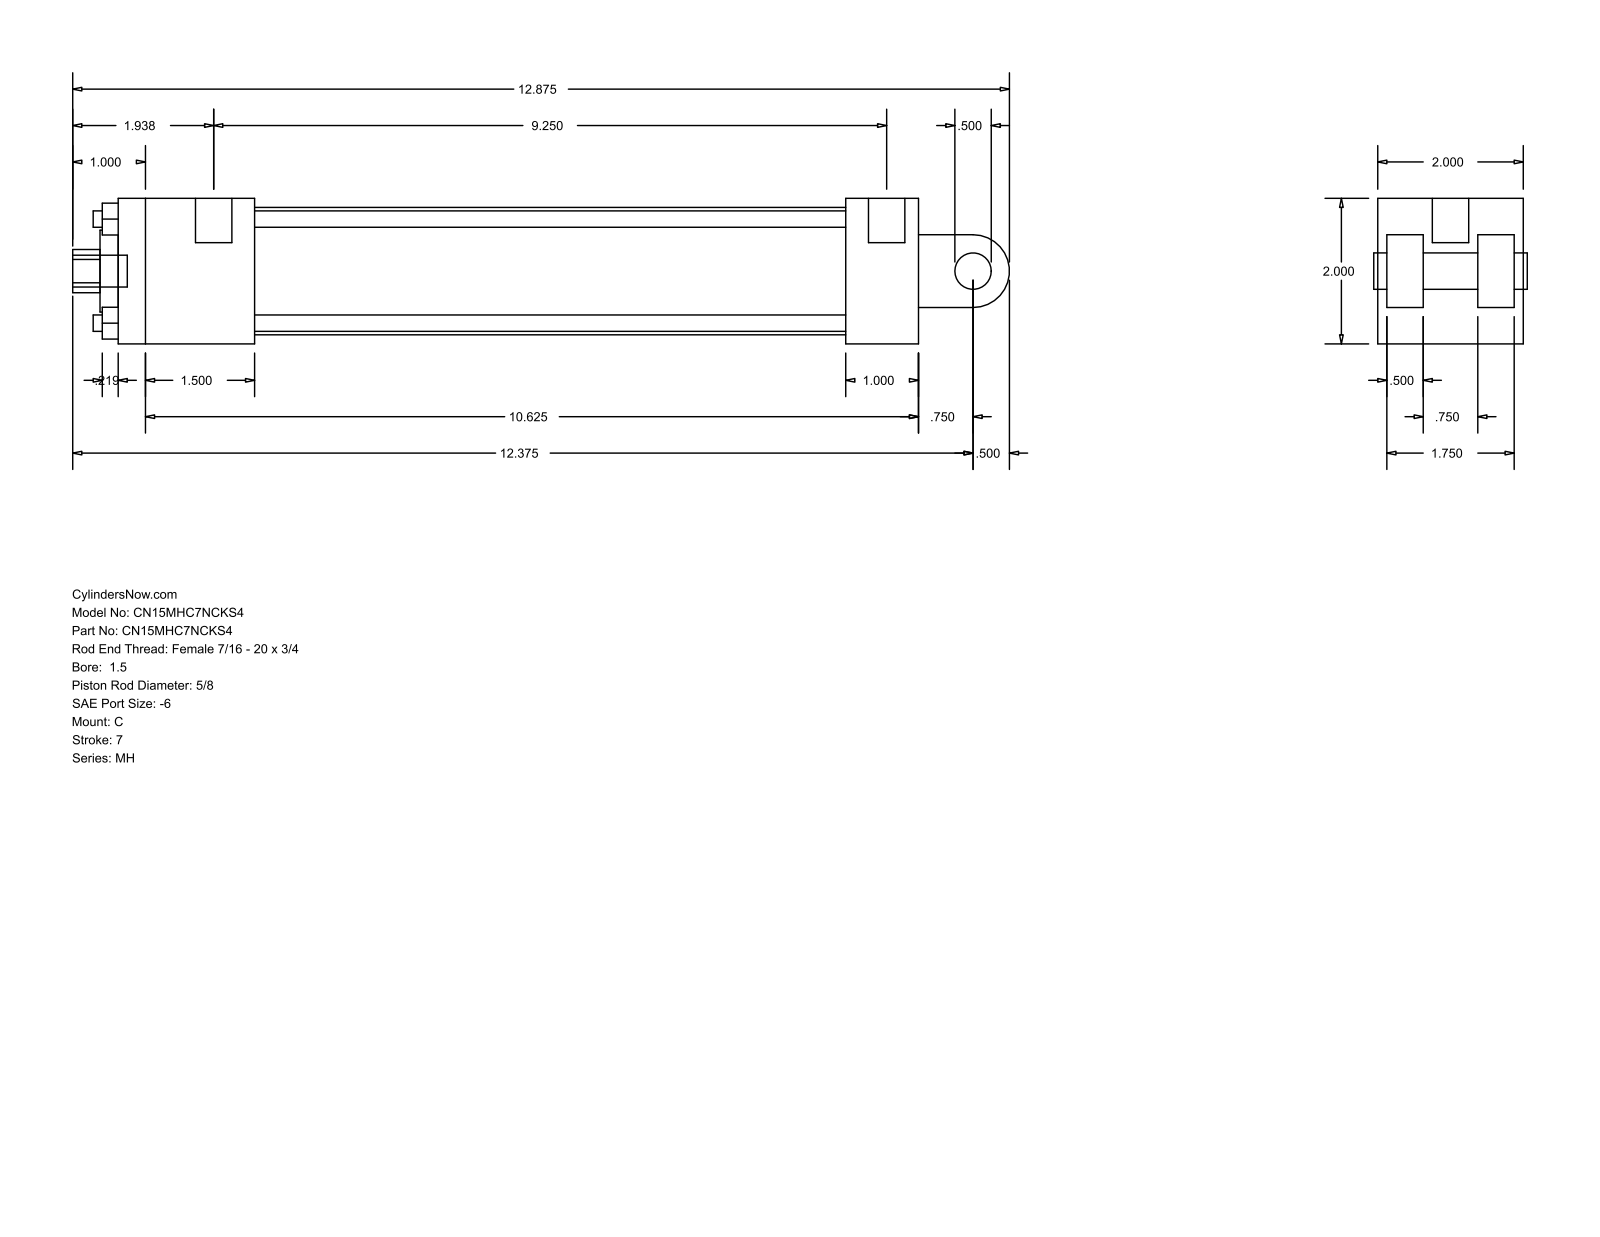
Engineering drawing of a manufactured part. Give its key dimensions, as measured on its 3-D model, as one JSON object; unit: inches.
{"part_name": "MH_C__0150_0.625", "step_written_by": "GSSL Pune (CONFIG_CONTROL_DESIGN)", "units": "inches", "bodies": {"solids": 0, "faces": 99, "planar": 70, "cylindrical": 29, "other": 0}, "overall_size": [12.875, 2, 2], "round_holes": [[0.225, 4], [0.219, 2], [0.5, 1], [0.625, 1], [1.125, 1], [1.75, 1]], "round_bosses_or_shafts": [[0.5, 2], [0.219, 2], [0.437, 1]], "partial_cylinders_radius": [[0.297, 1], [0.5, 1]], "face_to_face_distances": [2, 0.5, 11, 0.125, 0.625, 1.375, 1.875, 1.25, 1.5, 1.875], "hole_center_spacings": [1.011, 1.43, 2.022]}
